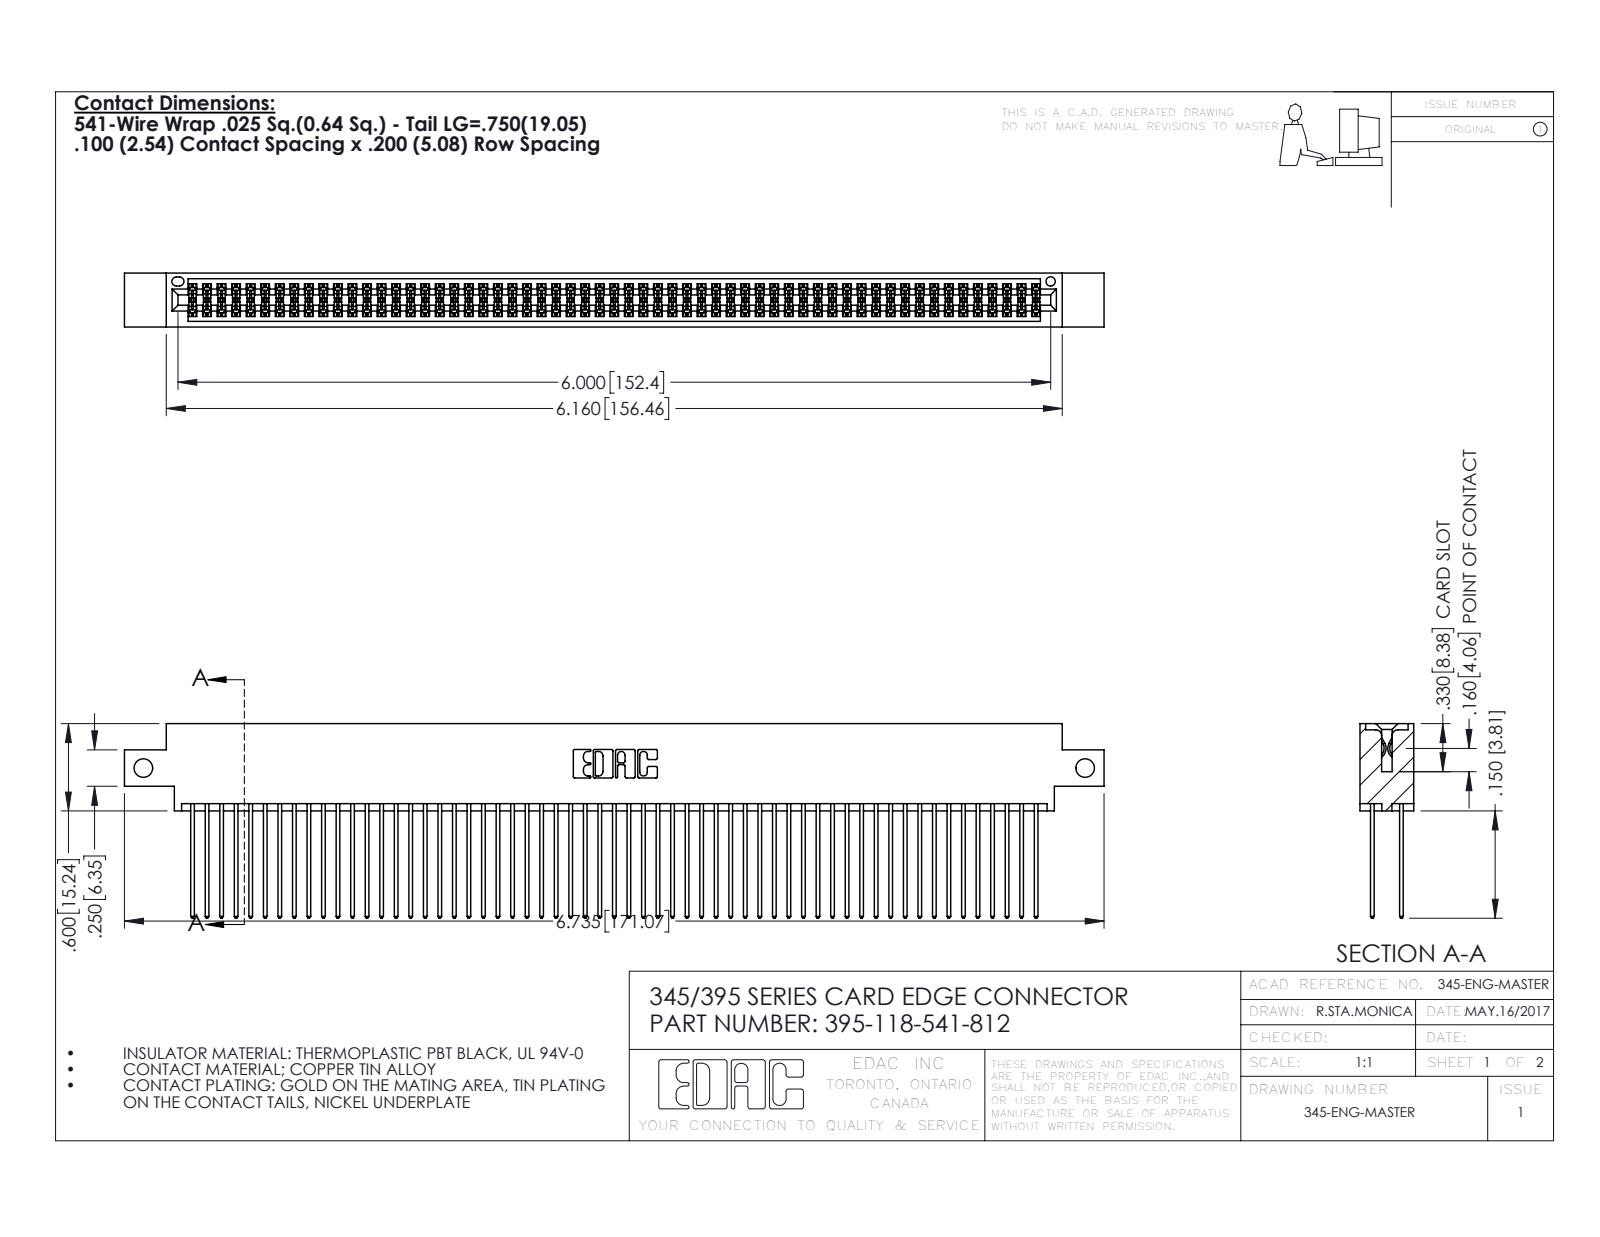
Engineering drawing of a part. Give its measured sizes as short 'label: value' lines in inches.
name: 345 Part_0.170 Offset - Side Mount; 395-118-541-812; 345-292-001_345-293-141
written by: SolidWorks 2016 (CONFIG_CONTROL_DESIGN)
unit: in
bodies: 119 solids, 6030 faces (3978 planar, 2052 cylindrical, 0 other)
size: 6.735 × 1.337 × 0.37
volume: 1.053 in³; area: 44.98 in²
holes: 2× ⌀0.128, 1× ⌀0.064
rounds: 177× R0.006, 118× R0.01, 22× R0.01, 6× R0.007, 6× R0.031, 3× R0.026, 2× R0.014, 2× R0.019
face distances: 0.298, 0.072, 0.2, 0.098, 0.272, 0.025, 0.225, 0.37, 0.175, 0.149
hole spacings: 6.475
